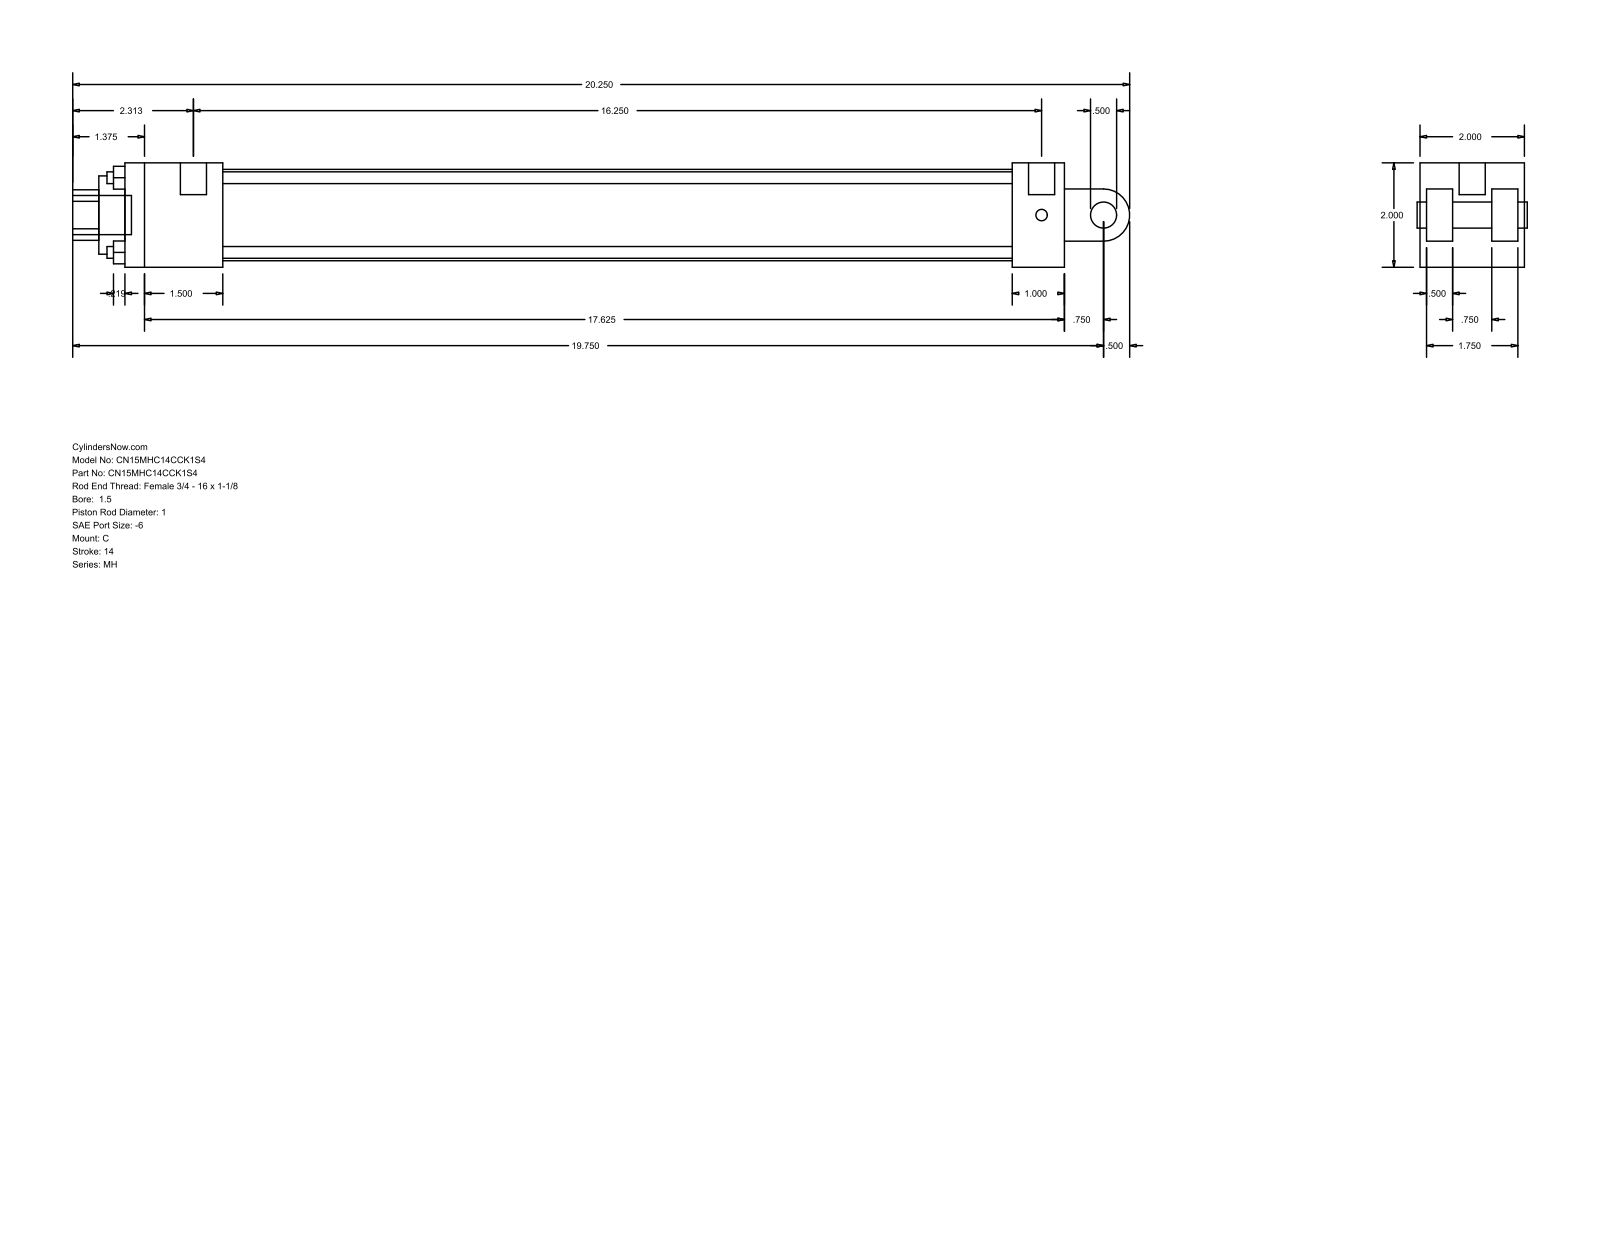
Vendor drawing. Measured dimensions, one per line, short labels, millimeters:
name: MH_C__0150_1
written by: GSSL Pune (CONFIG_CONTROL_DESIGN)
unit: mm
bodies: 0 solids, 99 faces (70 planar, 29 cylindrical, 0 other)
size: 514.35 × 50.8 × 50.8
holes: 4× ⌀5.71, 2× ⌀5.56, 1× ⌀12.7, 1× ⌀25.4, 1× ⌀38.1, 1× ⌀44.45
bosses: 2× ⌀12.7, 2× ⌀5.56, 1× ⌀19.05
rounds: 1× R12.29, 1× R12.7
face distances: 50.8, 12.7, 47.63, 3.17, 15.87, 25.4, 34.93, 31.76, 457.2, 38.1
hole spacings: 25.68, 36.32, 51.36
